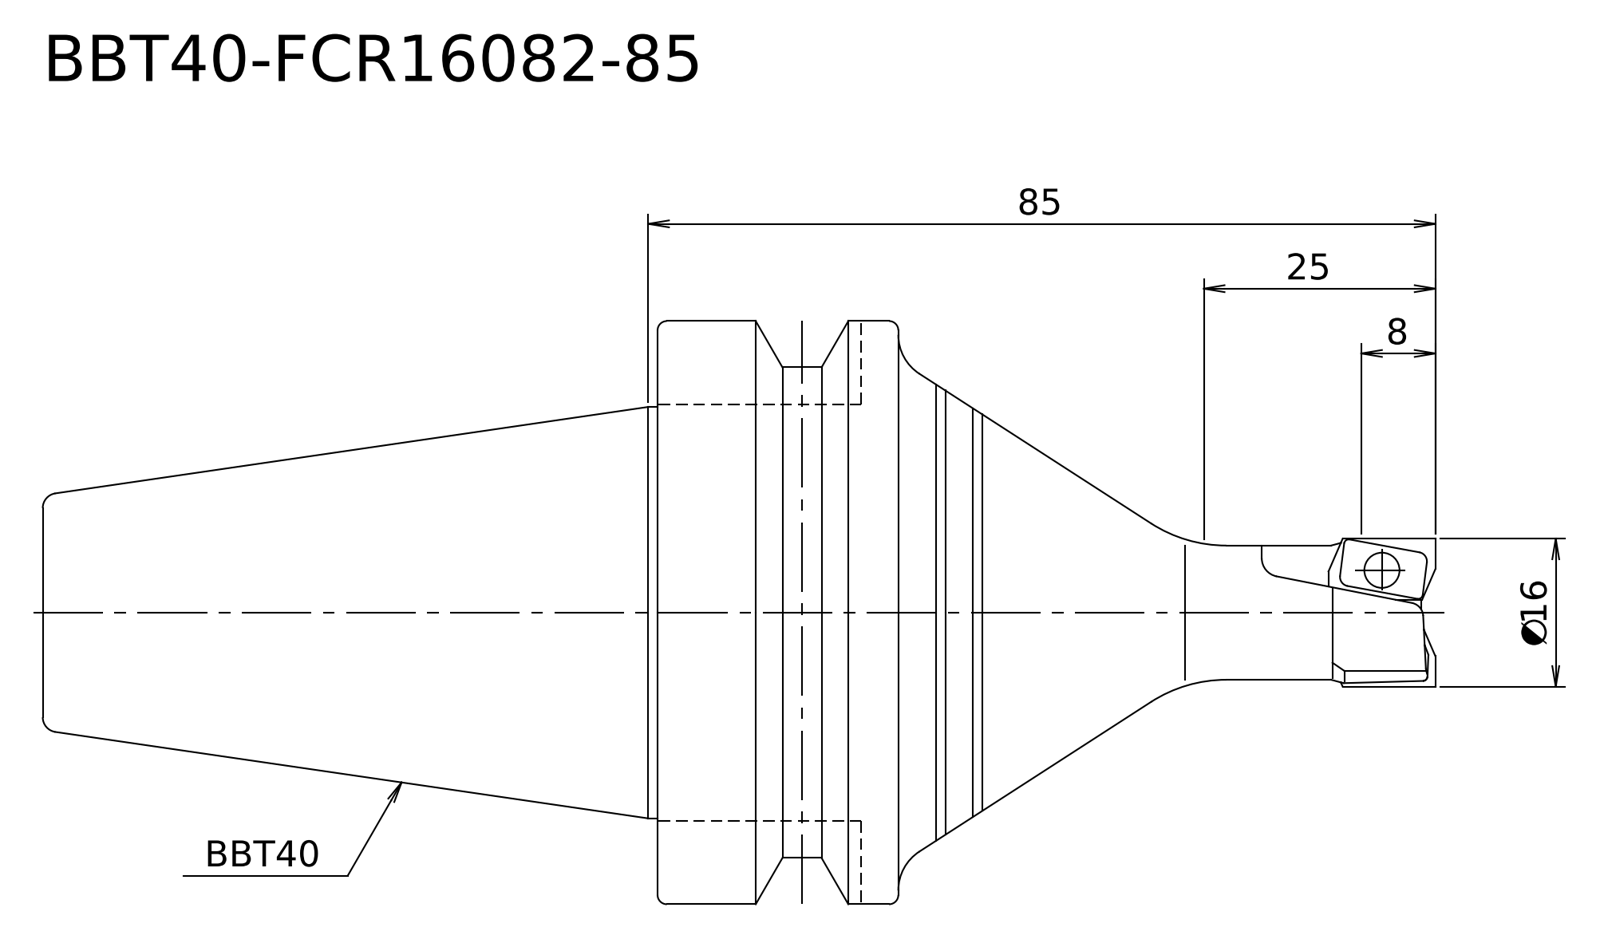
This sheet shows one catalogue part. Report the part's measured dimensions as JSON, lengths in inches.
{"step_written_by": "Kubotek KeyCreator V8.5.1 (14335) (CONFIG_CONTROL_DESIGN)", "units": "inches", "bodies": {"solids": 1, "faces": 17, "planar": 4, "cylindrical": 6, "other": 7}, "overall_size": [5.921, 2.48, 2.48], "volume_in3": 10.87, "surface_area_in2": 33.49, "round_bosses_or_shafts": [[2.48, 1], [2.087, 1], [1.75, 1], [0.63, 1], [0.571, 1]], "face_to_face_distances": [2.614, 1.024, 3.638, 2.283, 3.307, 5.921]}
